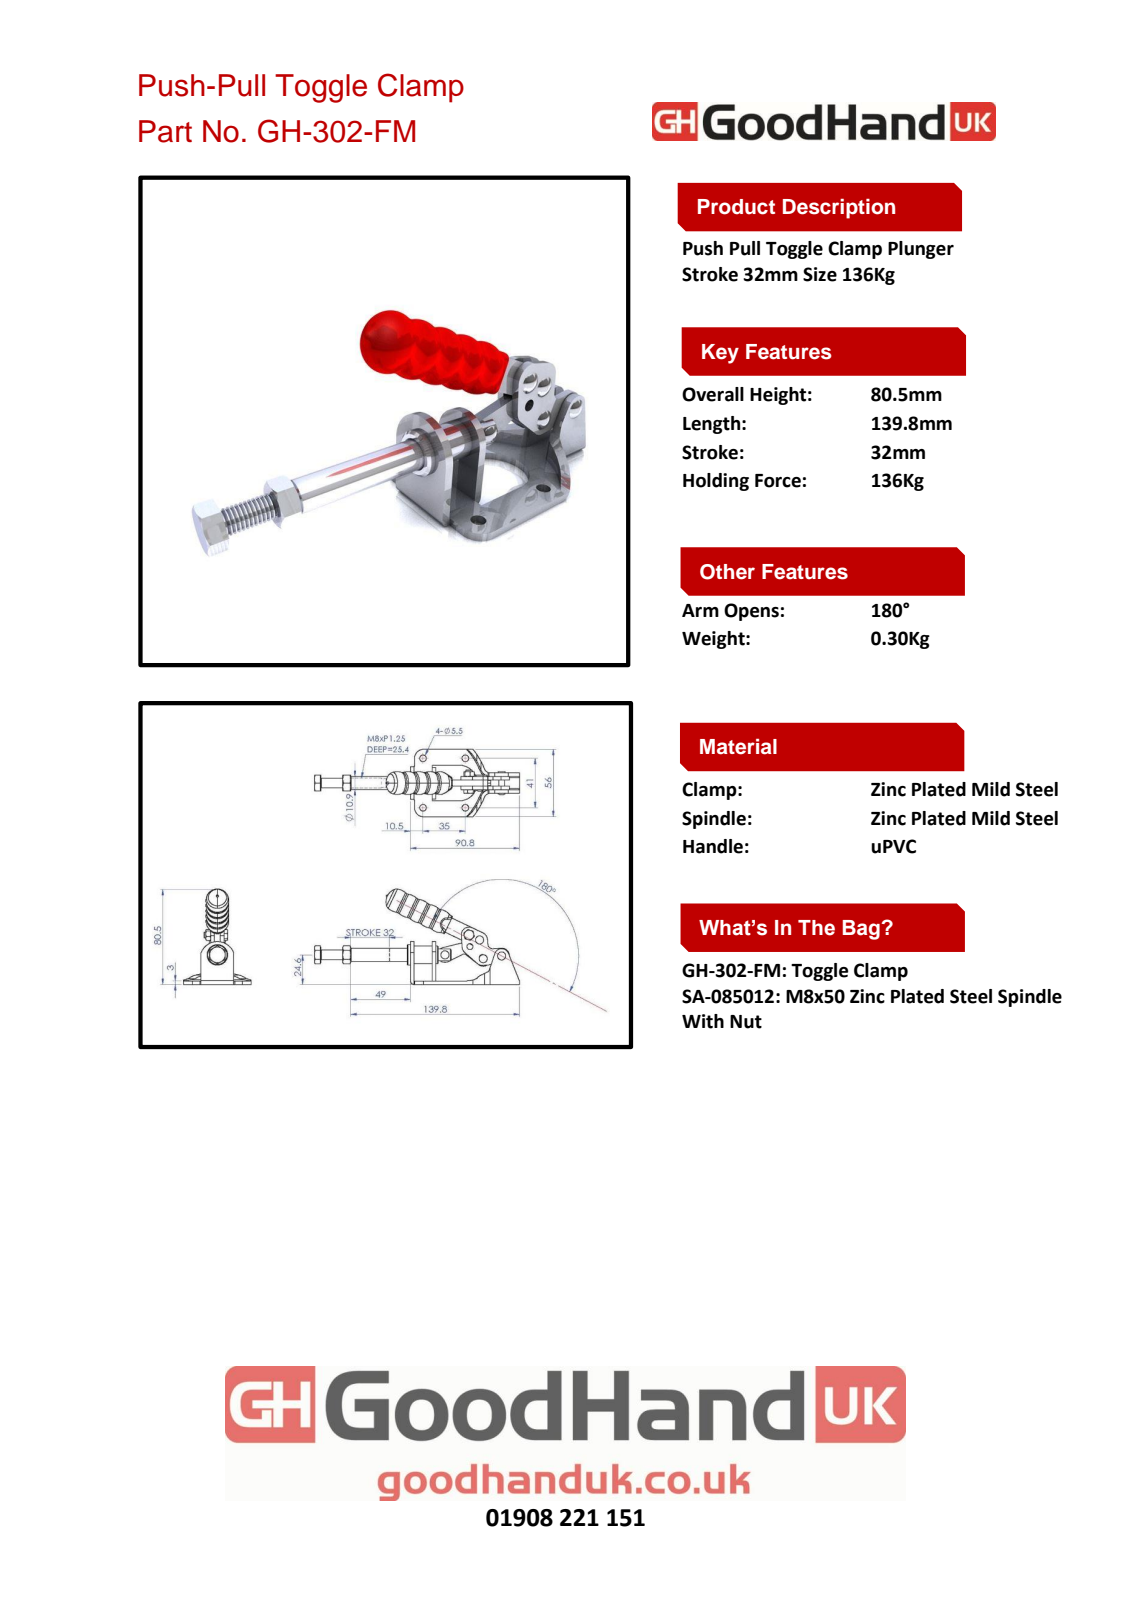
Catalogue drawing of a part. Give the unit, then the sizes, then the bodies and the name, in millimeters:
Units: millimetres
Overall size (bounding box): 170.4 × 81.52 × 56
Round holes (diameter × count): ⌀5.5 ×4, ⌀3 ×3, ⌀10.9 ×1
Round bosses / shafts (diameter × count): ⌀5.8 ×5, ⌀17 ×1, ⌀15.86 ×1, ⌀14.53 ×1, ⌀13 ×1, ⌀8 ×1, ⌀4.8 ×1
Partial cylindrical surfaces — rounded edges, fillets, slot ends (radius × count): R6.5 ×6, R1 ×4, R2 ×3, R5 ×2, R7.5 ×2, R8 ×2, R62 ×2, R65 ×2
Main face-to-face distances: 3, 11, 8, 18, 3.2, 7.8, 4.8, 6, 6.2, 10.8
Hole centre spacings: 35, 41, 53.91, 16.1, 31.8, 47.84
Volume: 50 141 mm³ · Surface area: 27 616 mm²
Bodies: 4 solids, 254 faces (100 planar, 104 cylindrical, 50 other)
Part name (STEP PRODUCT): Group4^493790(GH-302-FM); Group2^493790(GH-302-FM); GH-302-FM; Group1^493790(GH-302-FM) (+1 more)
STEP written by: SolidWorks 2016 (AUTOMOTIVE_DESIGN)
